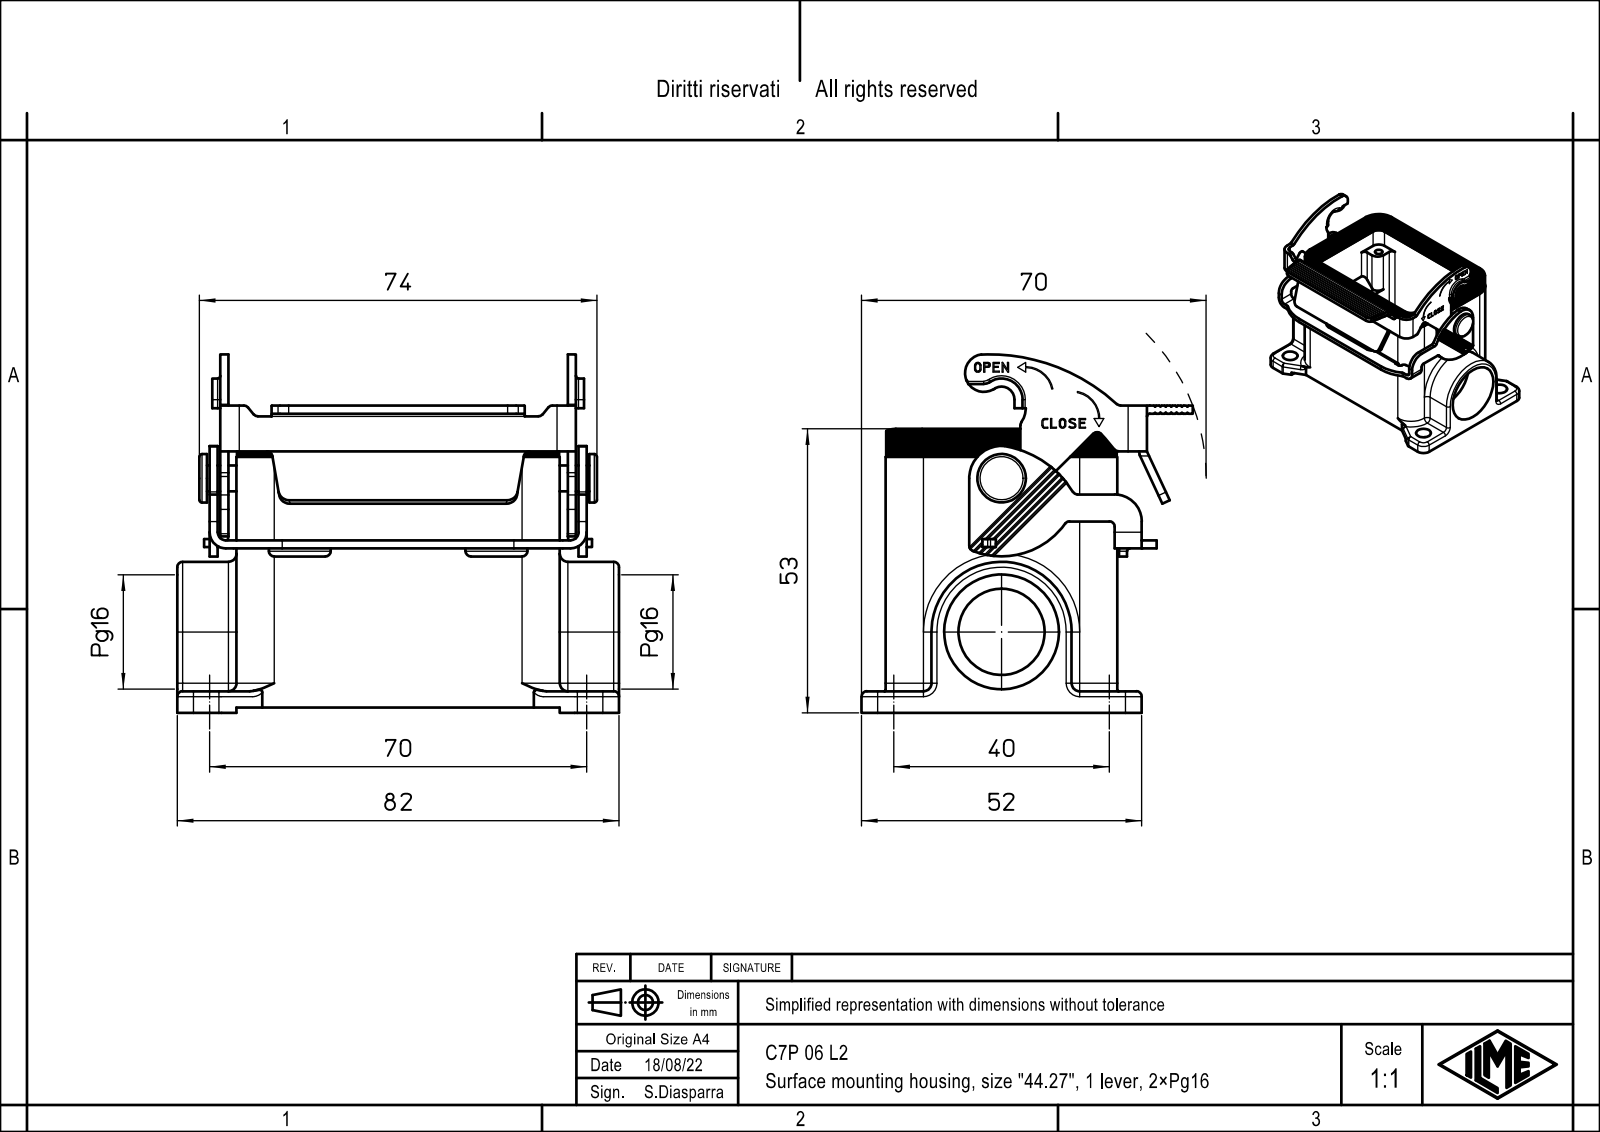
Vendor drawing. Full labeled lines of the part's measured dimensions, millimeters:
Part name (STEP PRODUCT): C7P 06 L2
STEP written by: Creo Elements/Direct Modeling 20.1B 02-Apr-2019 (C) Parametric Technology GmbH (AUTOMOTIVE_DESIGN)
Units: millimetres
Bodies: 1 solid, 1079 faces (790 planar, 225 cylindrical, 64 other)
Overall size (bounding box): 82 × 66.5 × 61.5
Volume: 63 772 mm³ · Surface area: 36 735 mm²
Round holes (diameter × count): ⌀2.75 ×4, ⌀5.5 ×4, ⌀16 ×1, ⌀21.3 ×1
Round bosses / shafts (diameter × count): ⌀9 ×1, ⌀4.8 ×1
Partial cylindrical surfaces — rounded edges, fillets, slot ends (radius × count): R1 ×48, R2 ×21, R1.5 ×17, R3 ×17, R0.5 ×8, R3.1 ×4, R3.5 ×4, R4 ×4
Main face-to-face distances: 3.75, 39.25, 1.5, 3, 43, 3.5, 2, 63, 35.5, 4
Hole centre spacings: 14.53, 35.93, 57.37, 66.12, 27, 40, 44, 51.62
